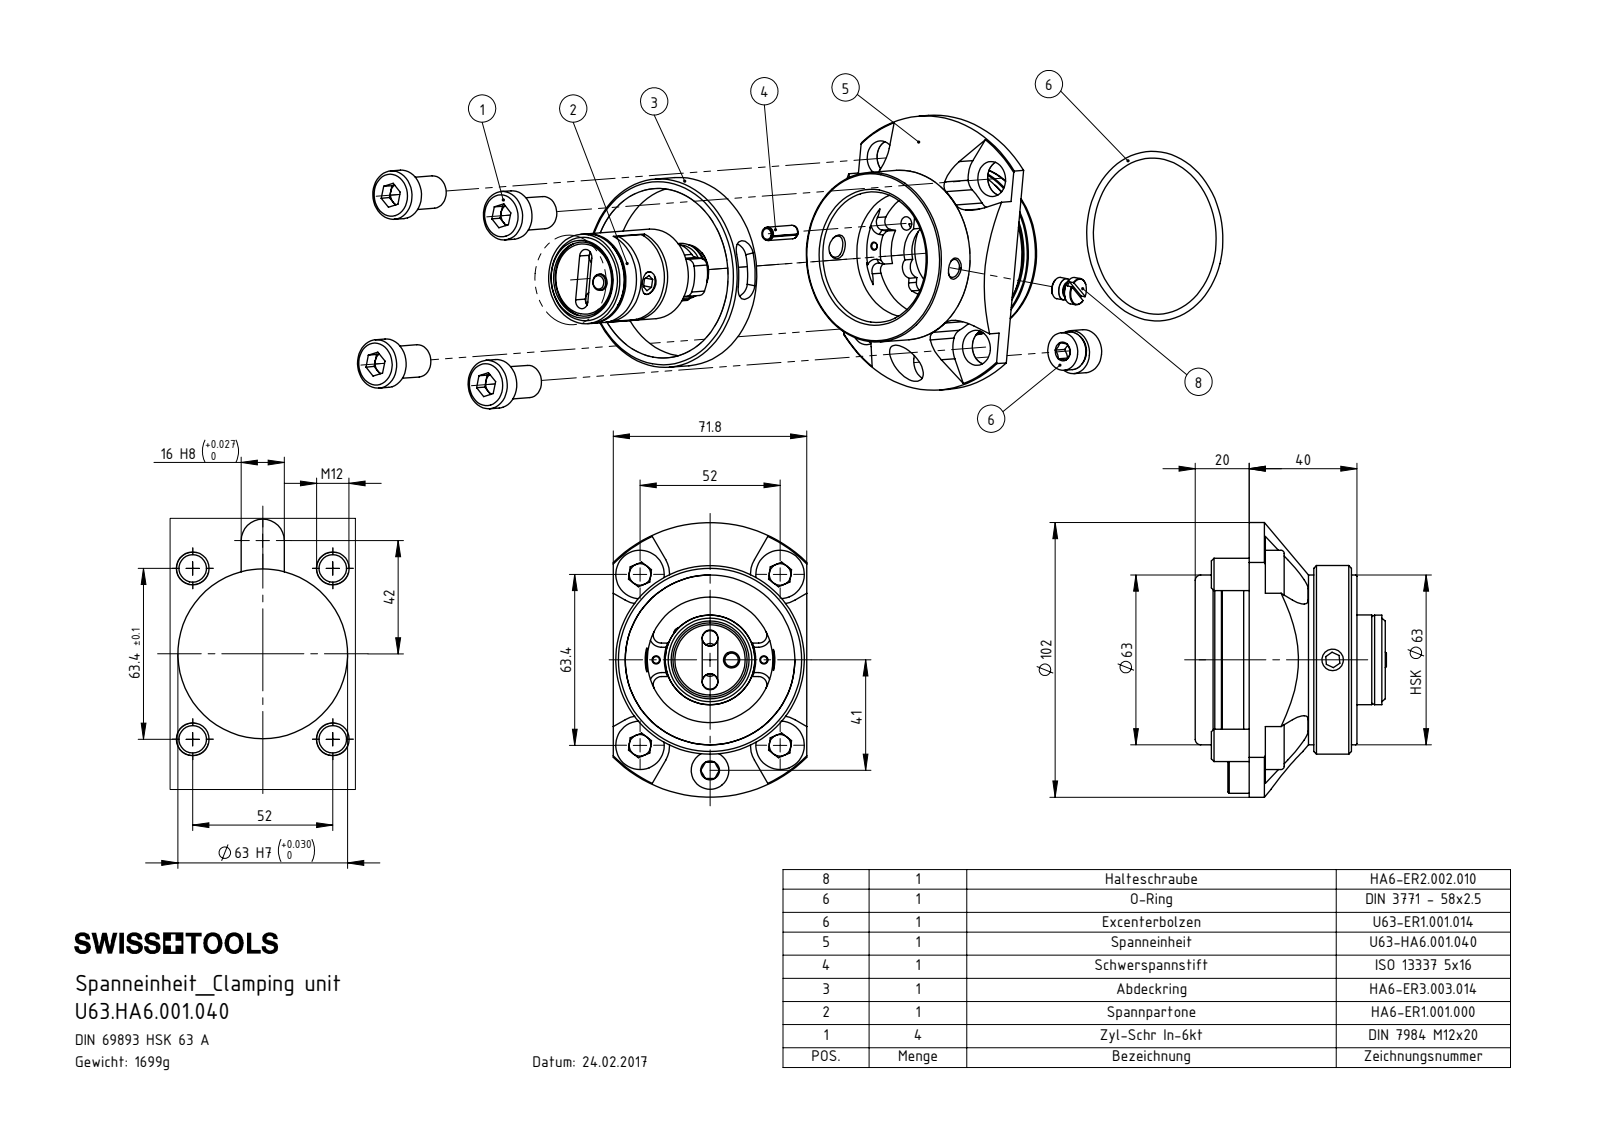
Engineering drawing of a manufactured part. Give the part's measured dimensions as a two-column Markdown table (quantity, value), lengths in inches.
| quantity | value |
| --- | --- |
| part name | U63-HA6.001.040_C; Backe6; Dichtung6; O-Ring (+8 more) |
| STEP written by | SolidWorks 2011 (AUTOMOTIVE_DESIGN) |
| units | inches |
| bodies | 17 solids, 496 faces (184 planar, 174 cylindrical, 138 other) |
| overall size | 4.012 × 2.827 × 2.776 |
| volume | 13.24 in³ |
| surface area | 110 in² |
| round holes (diameter × count) | 0.512 × 4, 0.098 × 2, 0.226 × 2, 0.228 × 2, 0.315 × 2, 0.335 × 2, 0.197 × 1, 0.236 × 1, 0.268 × 1, 0.394 × 1, 0.52 × 1, 0.551 × 1 |
| round bosses / shafts (diameter × count) | 0.709 × 4, 0.472 × 4, 2.756 × 1, 2.48 × 1, 2.461 × 1, 2.313 × 1, 1.311 × 1, 1.309 × 1 |
| partial cylindrical surfaces (radius × count) | 0.118 × 12, 0.197 × 8, 0.433 × 5, 0.114 × 4, 0.039 × 2, 0.113 × 2, 0.159 × 1, 0.61 × 1 |
| main face-to-face distances | 0.787, 0.236, 1.024, 1.339, 0.63, 0.26, 1.496, 1.575, 2.362, 0.055 |
| hole center spacings | 1.614, 1.27, 2.199, 0.315, 0.446, 0.478, 0.787, 1.087 |
